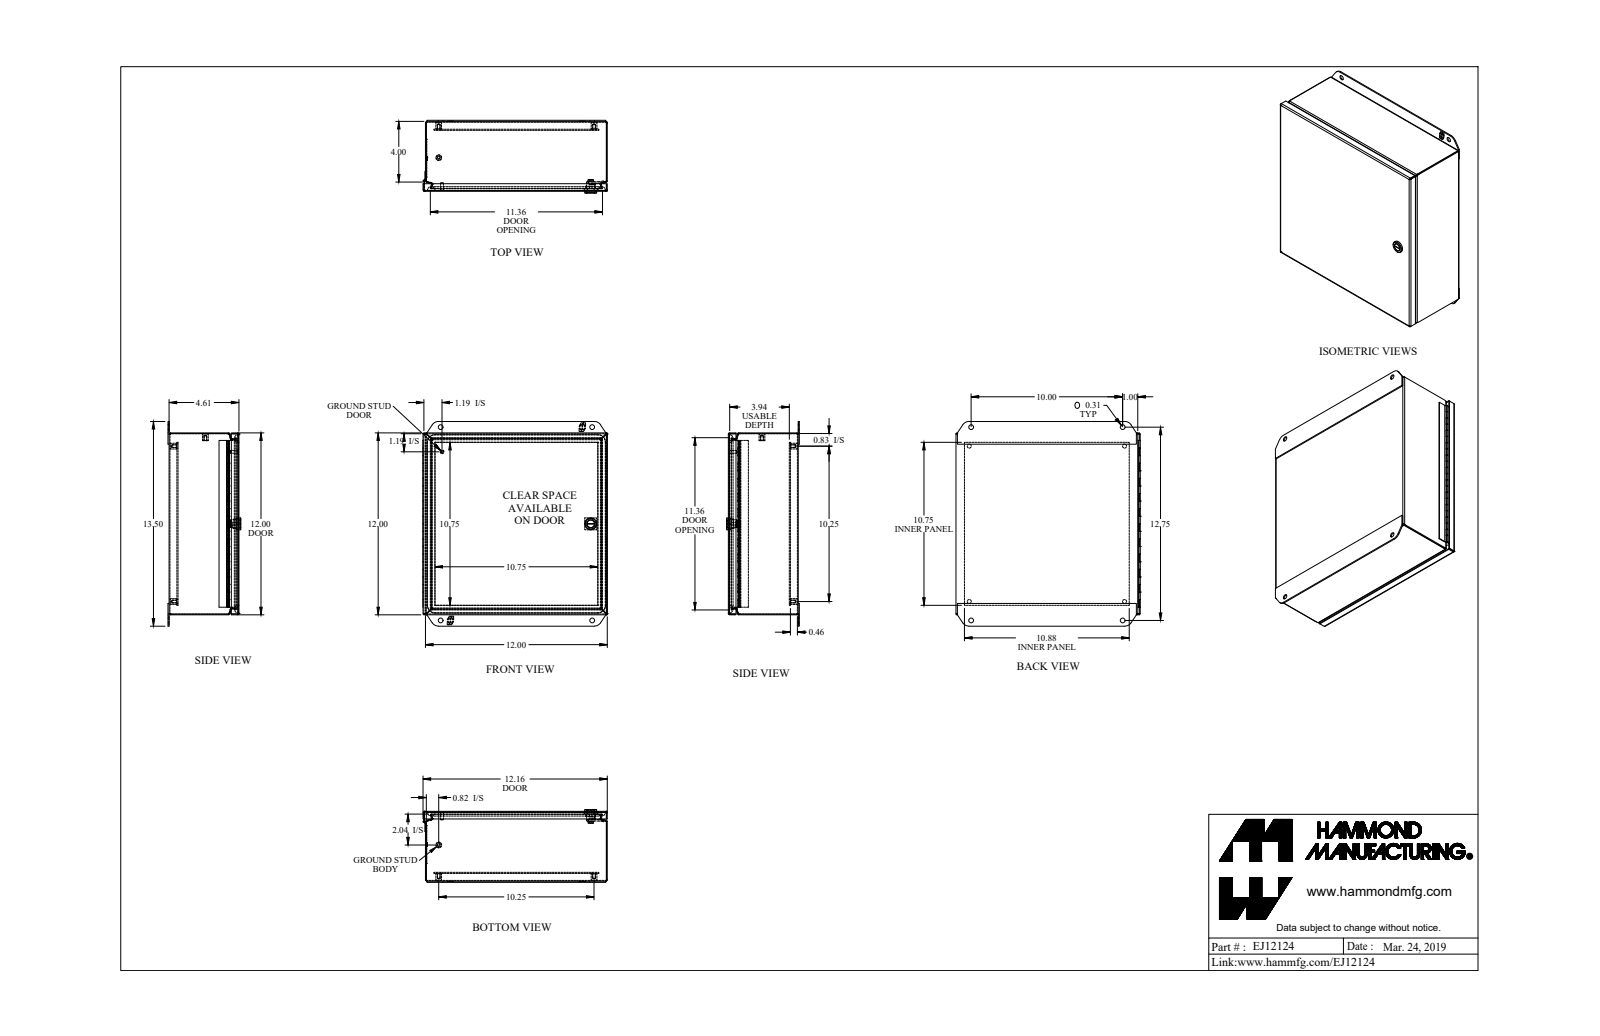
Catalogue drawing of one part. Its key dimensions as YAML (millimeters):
part_name: "EJ12124_Default"
step_written_by: "SolidWorks 2019 (CONFIG_CONTROL_DESIGN)"
units: millimeters
bodies: {solids: 16, faces: 707, planar: 393, cylindrical: 222, other: 92}
overall_size: [342.9, 309, 122]
volume: 760000
surface_area: 980000
round_holes:
  - {diameter: 4, count: 5}
  - {diameter: 6.7, count: 4}
  - {diameter: 8, count: 4}
  - {diameter: 1.3, count: 1}
  - {diameter: 13.1, count: 1}
round_bosses_or_shafts:
  - {diameter: 9.5, count: 5}
  - {diameter: 20, count: 1}
  - {diameter: 13.6, count: 1}
  - {diameter: 12.6, count: 1}
  - {diameter: 11, count: 1}
  - {diameter: 6.4, count: 1}
  - {diameter: 4.8, count: 1}
  - {diameter: 2.5, count: 1}
partial_cylinders:
  - {radius: 0.7, count: 16}
  - {radius: 2.2, count: 16}
  - {radius: 7.1, count: 10}
  - {radius: 6.4, count: 4}
  - {radius: 12.7, count: 4}
  - {radius: 12.7, count: 4}
  - {radius: 1.5, count: 2}
  - {radius: 13.7, count: 2}
face_to_face_distances: [1.4, 115.7, 303.4, 1.8, 15, 117.1, 114.2, 11.7, 13.1, 104]
hole_center_spacings: [260.4, 130.3, 259.1, 368.2, 389.2, 31.9, 31.9, 292.1]
